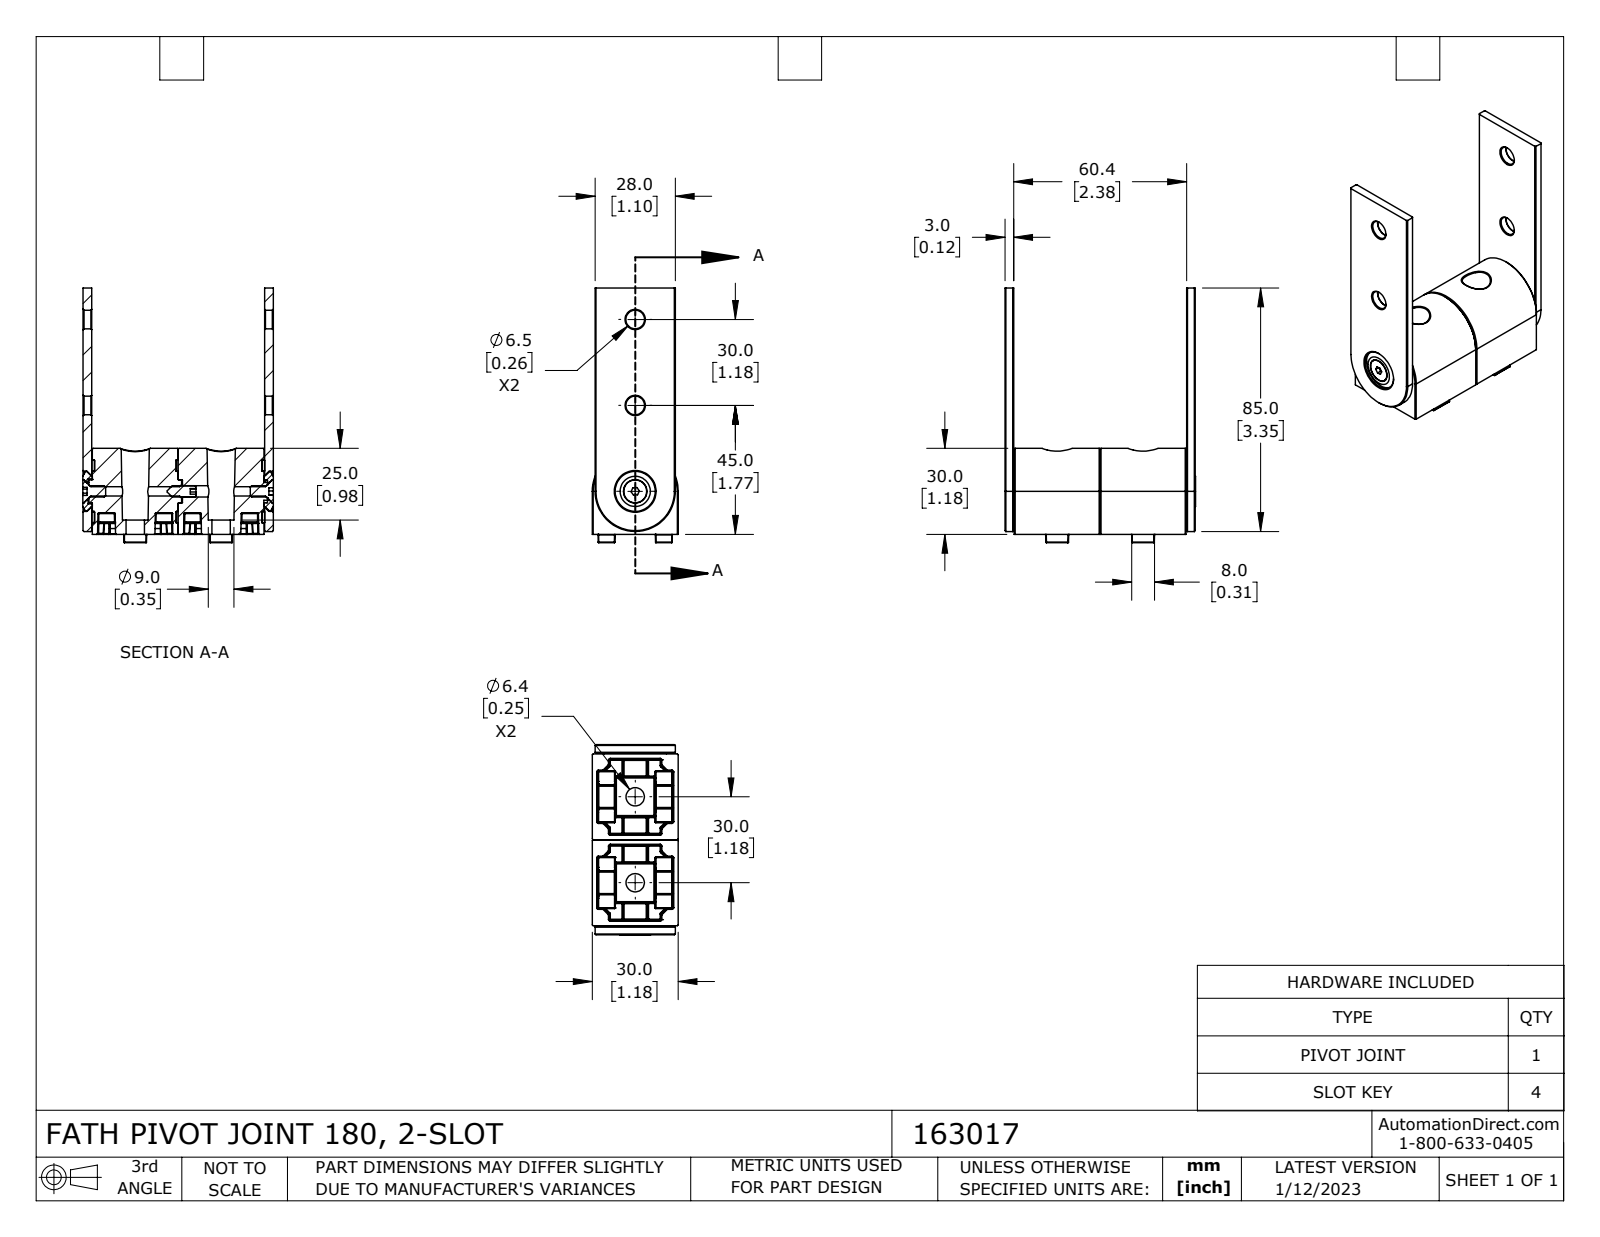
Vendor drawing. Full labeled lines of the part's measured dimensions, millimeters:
Part name (STEP PRODUCT): 163017
STEP written by: SolidWorks 2021 (CONFIG_CONTROL_DESIGN)
Units: millimetres
Bodies: 15 solids, 1552 faces (349 planar, 566 cylindrical, 637 other)
Overall size (bounding box): 88.9 × 66.5 × 30
Volume: 55 080 mm³ · Surface area: 28 370 mm²
Round holes (diameter × count): ⌀1.5 ×2, ⌀6.4 ×2, ⌀6.5 ×2, ⌀3.3 ×1, ⌀3.9 ×1, ⌀6.2 ×1, ⌀8.2 ×1, ⌀11 ×1, ⌀14.2 ×1, ⌀22 ×1
Round bosses / shafts (diameter × count): ⌀21.8 ×1, ⌀14 ×1, ⌀8 ×1, ⌀4 ×1
Partial cylindrical surfaces — rounded edges, fillets, slot ends (radius × count): R0.3 ×148, R0.2 ×120, R0.2 ×16, R1.2 ×2, R14 ×1, R15 ×1
Main face-to-face distances: 3, 63.4, 30, 30.2, 33.2, 60.4, 66.4, 1, 63.2, 3.2
Hole centre spacings: 30, 9, 31.3, 60.7, 18, 60
